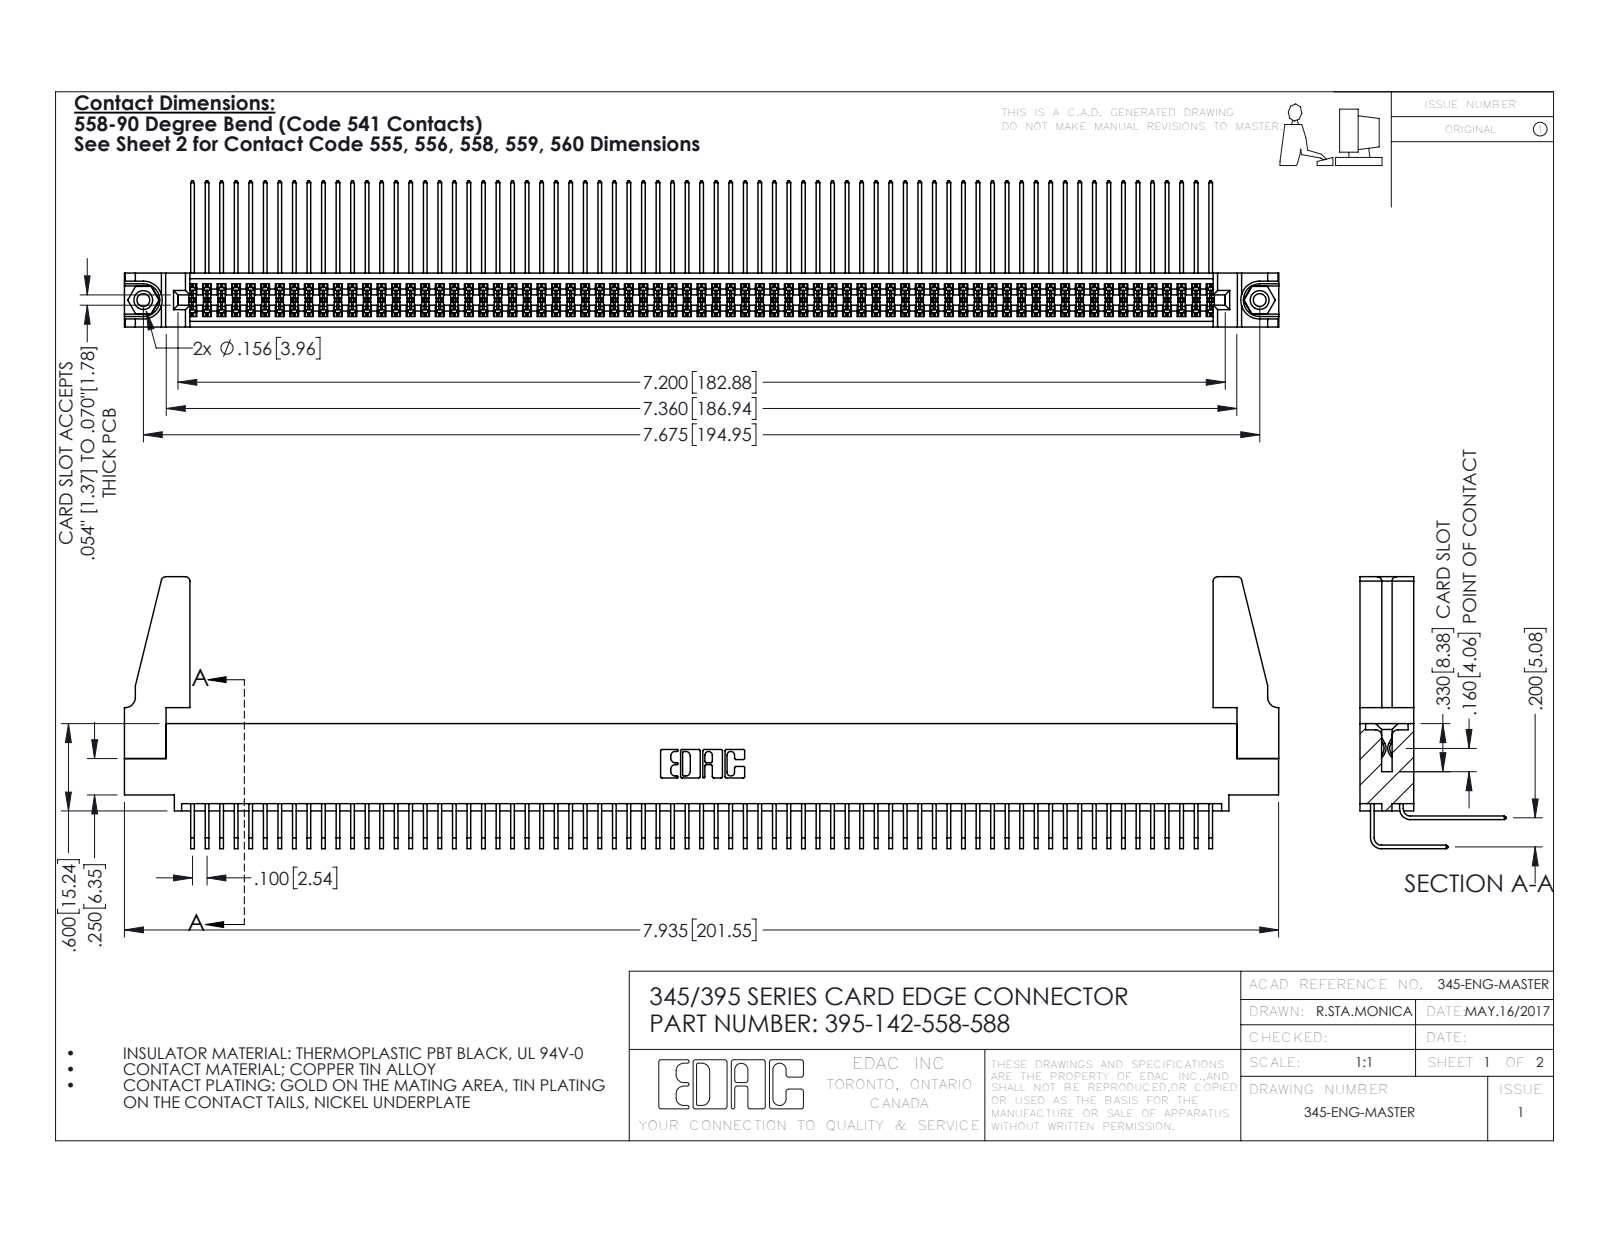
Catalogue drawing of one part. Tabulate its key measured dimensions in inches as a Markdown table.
| quantity | value |
| --- | --- |
| part name | 345-220-078_345-220-088; 345-250-001_345-250-001-102; 395-142-558-588; 345-292-001_558 Tail - 2 (+2 more) |
| STEP written by | SolidWorks 2016 (CONFIG_CONTROL_DESIGN) |
| units | inches |
| bodies | 147 solids, 7638 faces (5126 planar, 2496 cylindrical, 16 other) |
| overall size | 7.936 × 1.869 × 1.005 |
| volume | 1.455 in³ |
| surface area | 59.01 in² |
| round holes (diameter × count) | 0.089 × 2, 0.125 × 2, 0.156 × 2, 0.064 × 1 |
| round bosses / shafts (diameter × count) | 0.155 × 2 |
| partial cylindrical surfaces (radius × count) | 0.006 × 283, 0.01 × 22, 0.03 × 8, 0.007 × 6, 0.031 × 6, 0.026 × 3, 0.014 × 2, 0.019 × 2 |
| main face-to-face distances | 0.072, 0.298, 0.2, 0.37, 0.098, 0.272, 0.025, 0.225, 0.025, 0.175 |
| hole center spacings | 0.27, 7.439, 7.675 |
